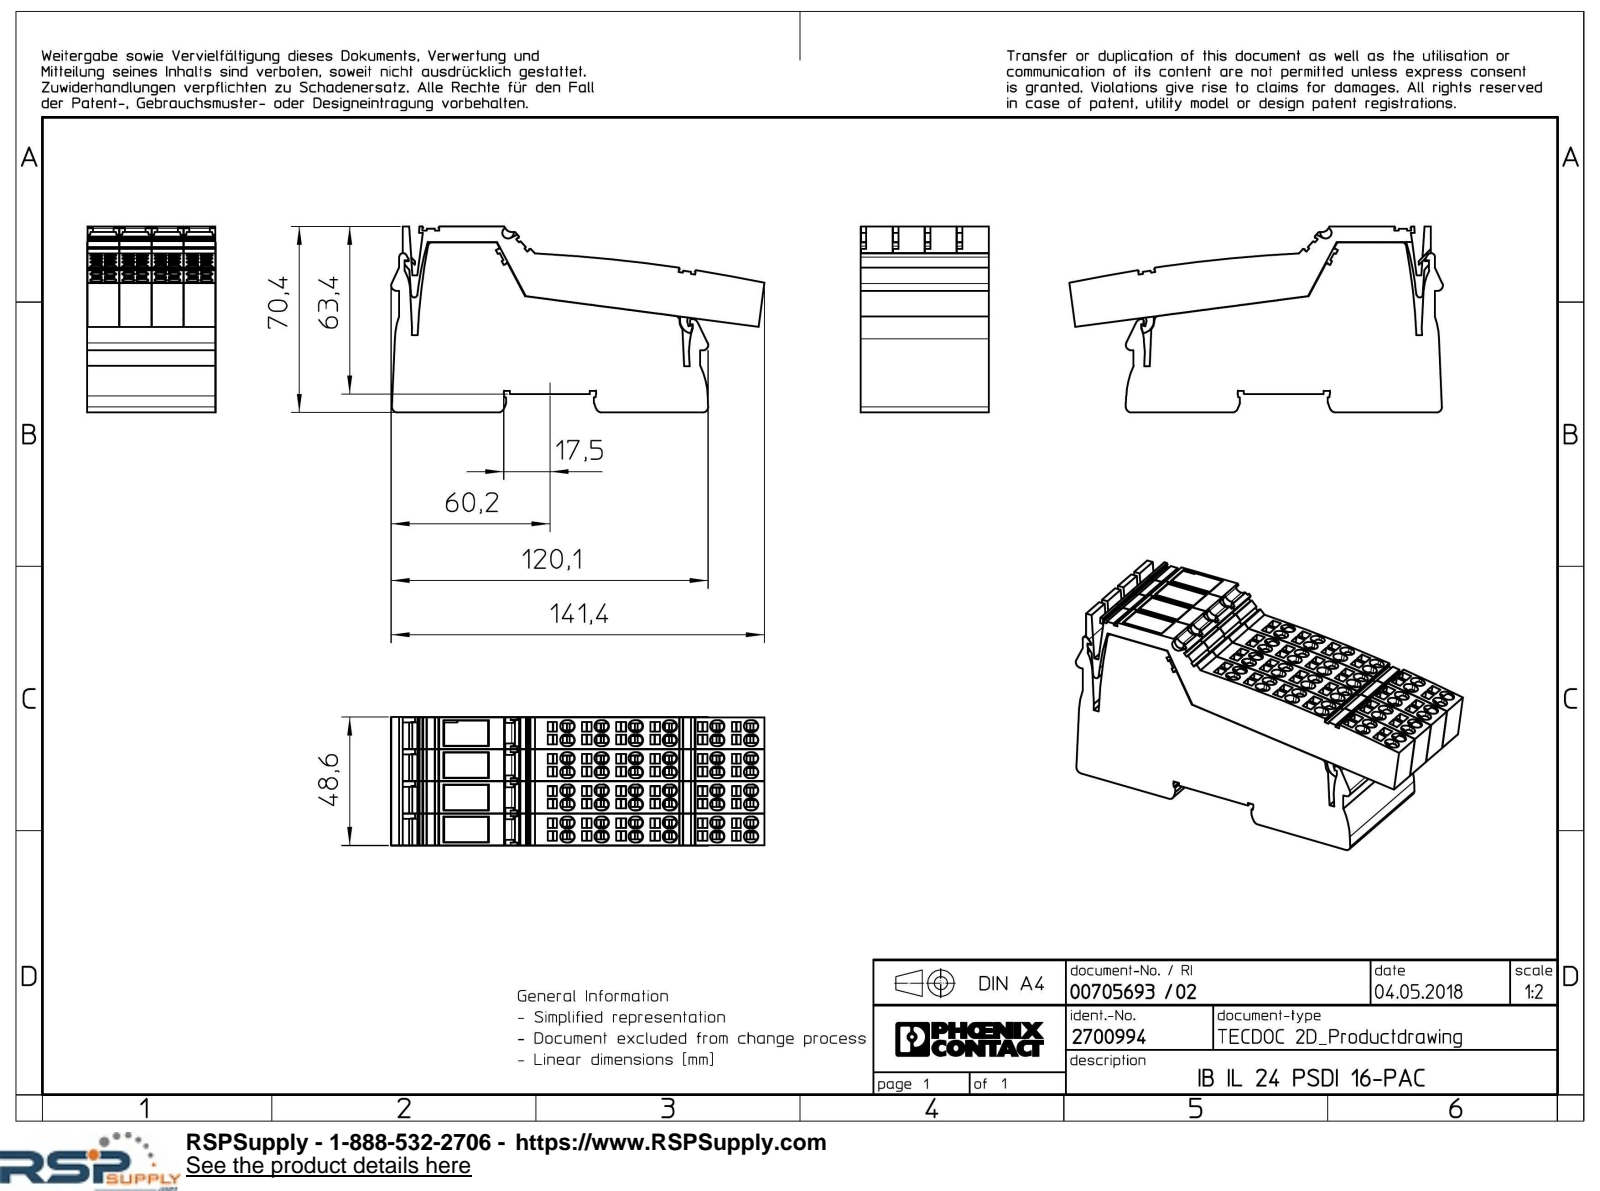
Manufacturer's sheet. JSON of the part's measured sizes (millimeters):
{"part_name": "L_L_ST_R_YE_1018-select; L_L_8_GEH_YE_1018-select; L_L_LWL_HBU-select; L-L_LWL_HBU_AUSSEN-select (+1 more)", "step_written_by": "Creo Elements/Direct Modeling 20.1A 29-Sep-2018 (C) Parametric Technology GmbH (AUTOMOTIVE_DESIGN)", "units": "millimeters", "bodies": {"solids": 9, "faces": 2413, "planar": 2088, "cylindrical": 213, "other": 112}, "overall_size": [141.41, 70.43, 48.6], "volume_mm3": 338274, "surface_area_mm2": 90655, "round_holes": [[1.2, 24]], "partial_cylinders_radius": [[2.25, 96], [0.6, 8], [2, 6], [0.15, 2], [1.7, 2], [8.5, 2], [9.5, 2], [16.7, 2]], "face_to_face_distances": [12.15, 24.3, 12, 24.15, 48.6, 36.45, 12.3, 36.3, 36.4, 36.5], "hole_center_spacings": [12.15, 4.8, 17.79, 17.8, 21.36, 24.3, 28.69, 7.35]}
